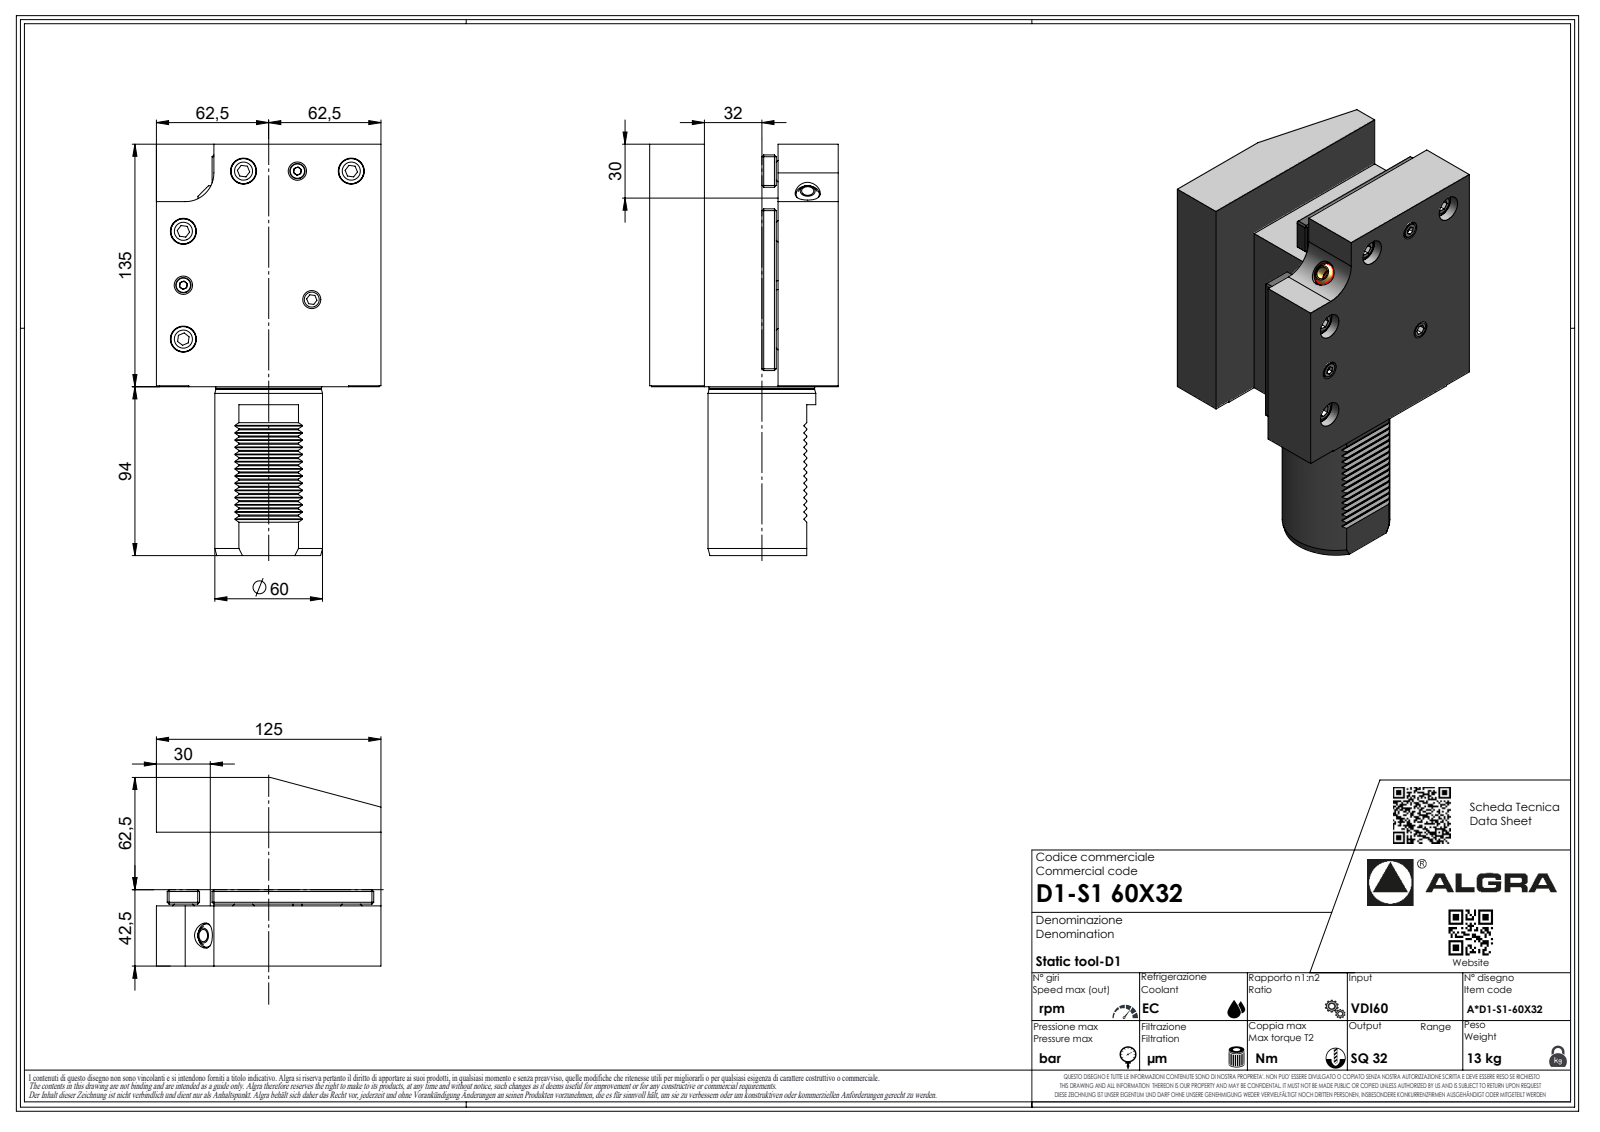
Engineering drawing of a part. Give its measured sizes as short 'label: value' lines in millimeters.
name: D1-S160X32
written by: SolidWorks 2023 (AUTOMOTIVE_DESIGN)
unit: mm
bodies: 1 solid, 389 faces (271 planar, 47 cylindrical, 71 other)
size: 229 × 125 × 105
volume: 1 670 000 mm³; area: 114 506 mm²
holes: 1× ⌀2.1, 1× ⌀8.5
bosses: 1× ⌀60, 1× ⌀58.7, 1× ⌀6.37, 1× ⌀1.7
rounds: 14× R0.3, 7× R0.33, 7× R0.52, 7× R3.7, 1× R0.21, 1× R16, 1× R61.5
face distances: 105, 30, 125, 30.5, 74.5, 135, 95, 32, 71.5, 41
